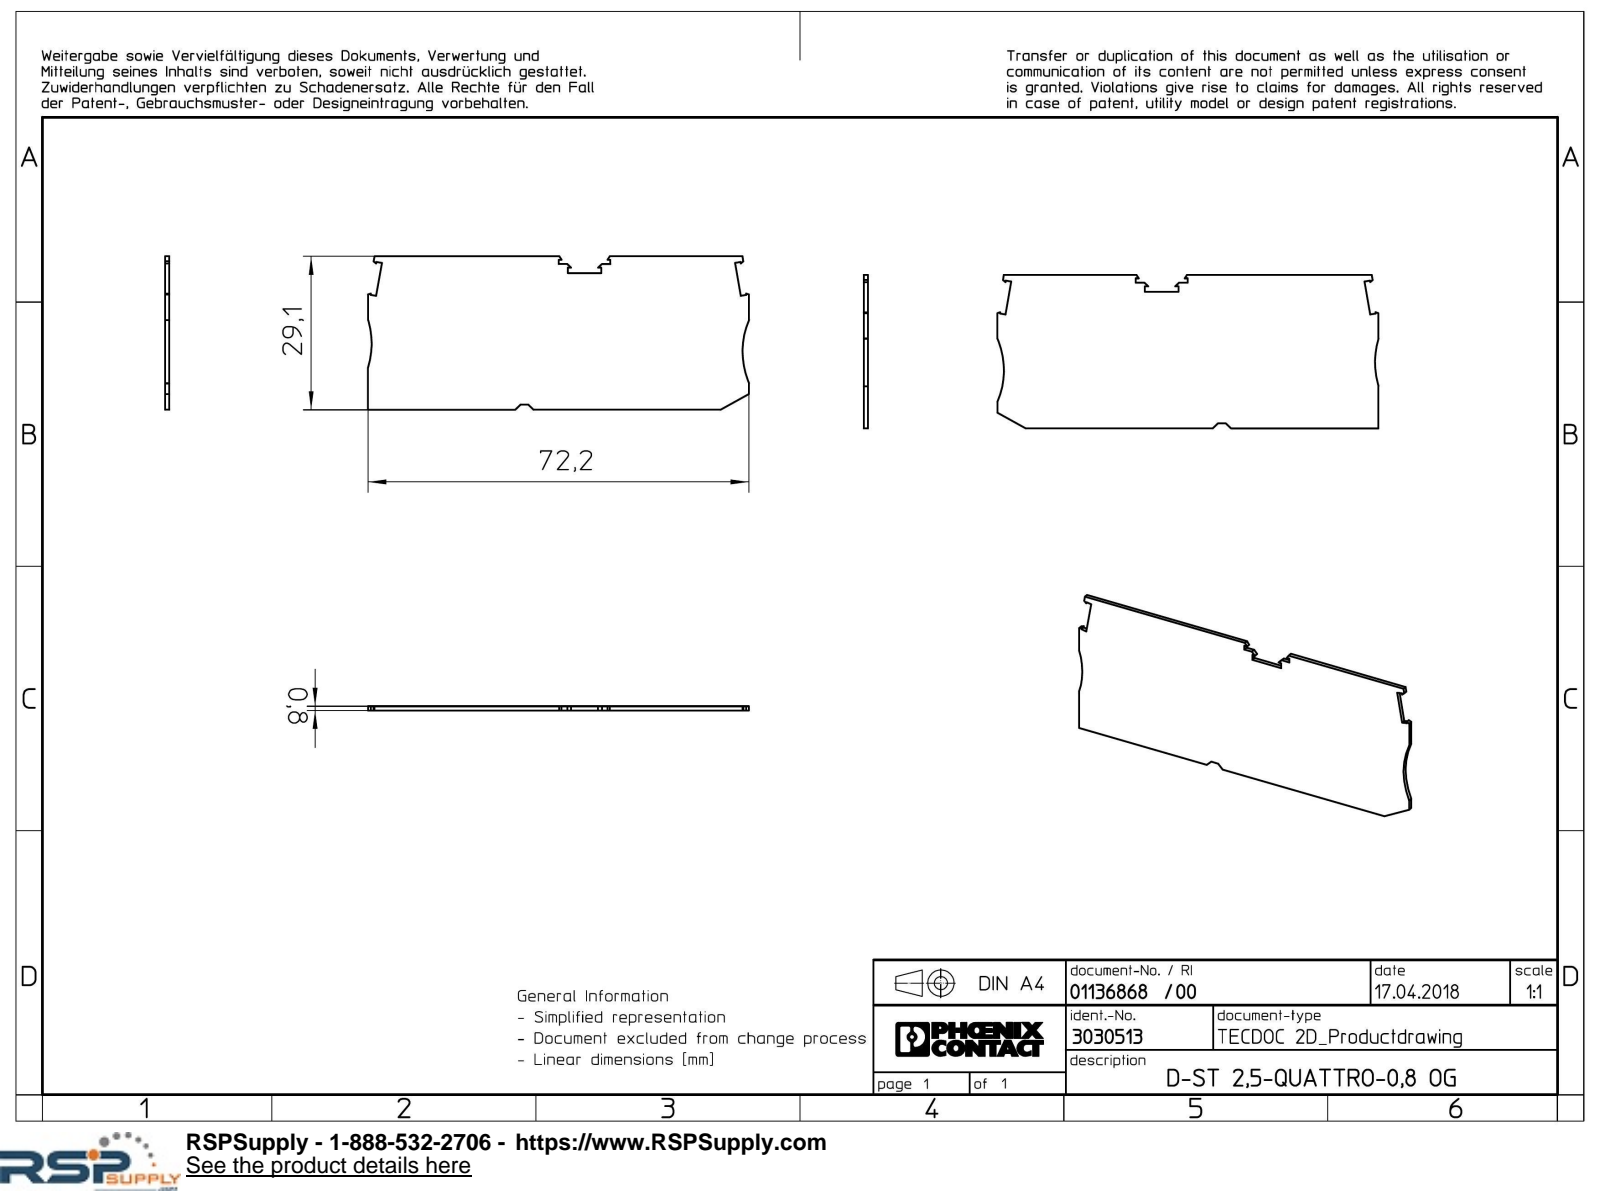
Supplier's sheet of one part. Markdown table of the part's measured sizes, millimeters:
| quantity | value |
| --- | --- |
| part name | D_ST_2.5_QUATTRO_0.8_OG-select |
| STEP written by | Creo Elements/Direct Modeling 18.1I 14-Aug-2016 (C) Parametric Technology GmbH (AUTOMOTIVE_DESIGN) |
| units | millimeters |
| bodies | 1 solid, 48 faces (46 planar, 2 cylindrical, 0 other) |
| overall size | 72.2 × 29.05 × 0.8 |
| volume | 1 615 mm³ |
| surface area | 4 212 mm² |
| partial cylindrical surfaces (radius × count) | 15 × 2 |
| main face-to-face distances | 0.8, 29.05, 72.2, 25.85, 3.2, 27.6, 1.75, 1.45, 1, 24.85 |
